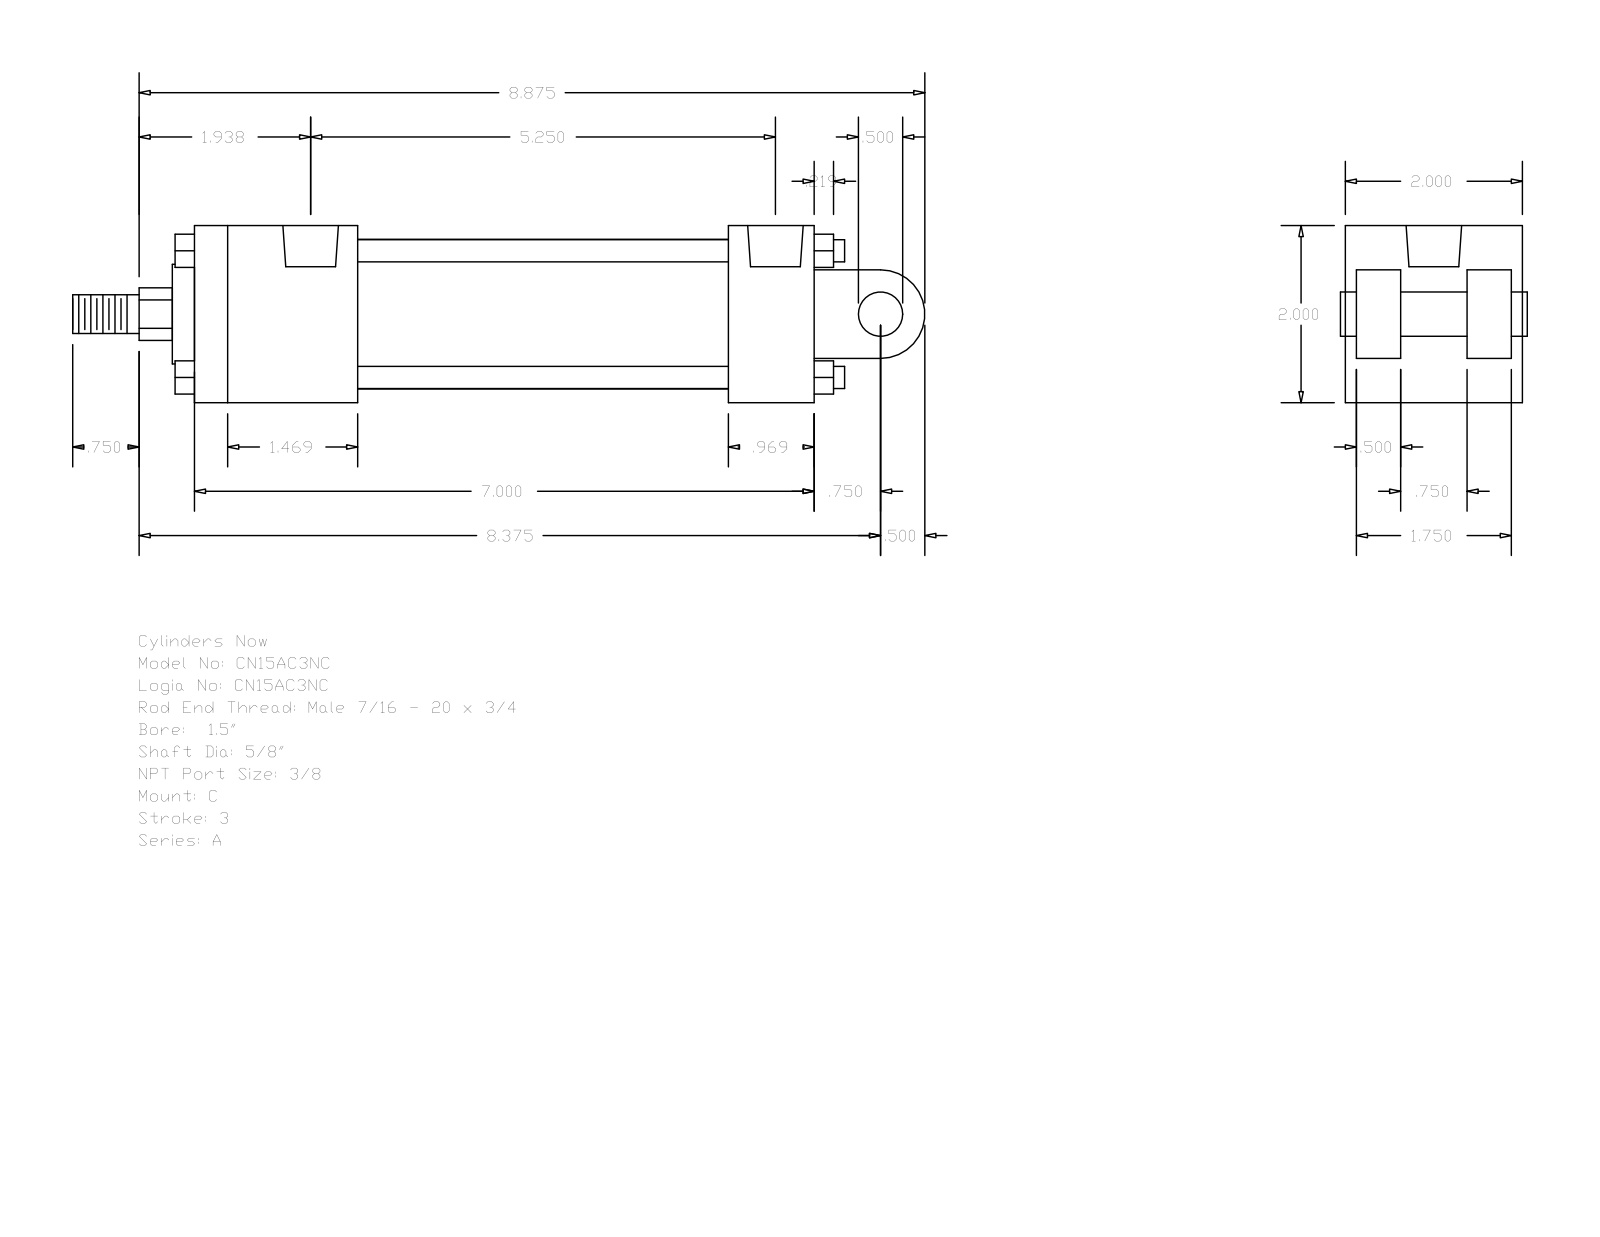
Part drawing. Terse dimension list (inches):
name: A_C__0150_0.625
written by: GSSL Pune (CONFIG_CONTROL_DESIGN)
unit: in
bodies: 0 solids, 135 faces (102 planar, 33 cylindrical, 0 other)
size: 9.625 × 2 × 2
holes: 4× ⌀0.219, 2× ⌀0.627
bosses: 4× ⌀0.25, 1× ⌀1.69, 1× ⌀1.125, 1× ⌀0.625, 1× ⌀0.5, 1× ⌀0.437
rounds: 1× R0.297, 1× R0.5
face distances: 2, 0.5, 7, 1.375, 0.125, 1.875, 0.625, 1.25, 6.031, 0.969
hole spacings: 0.156, 4.937, 5.094, 5.25
